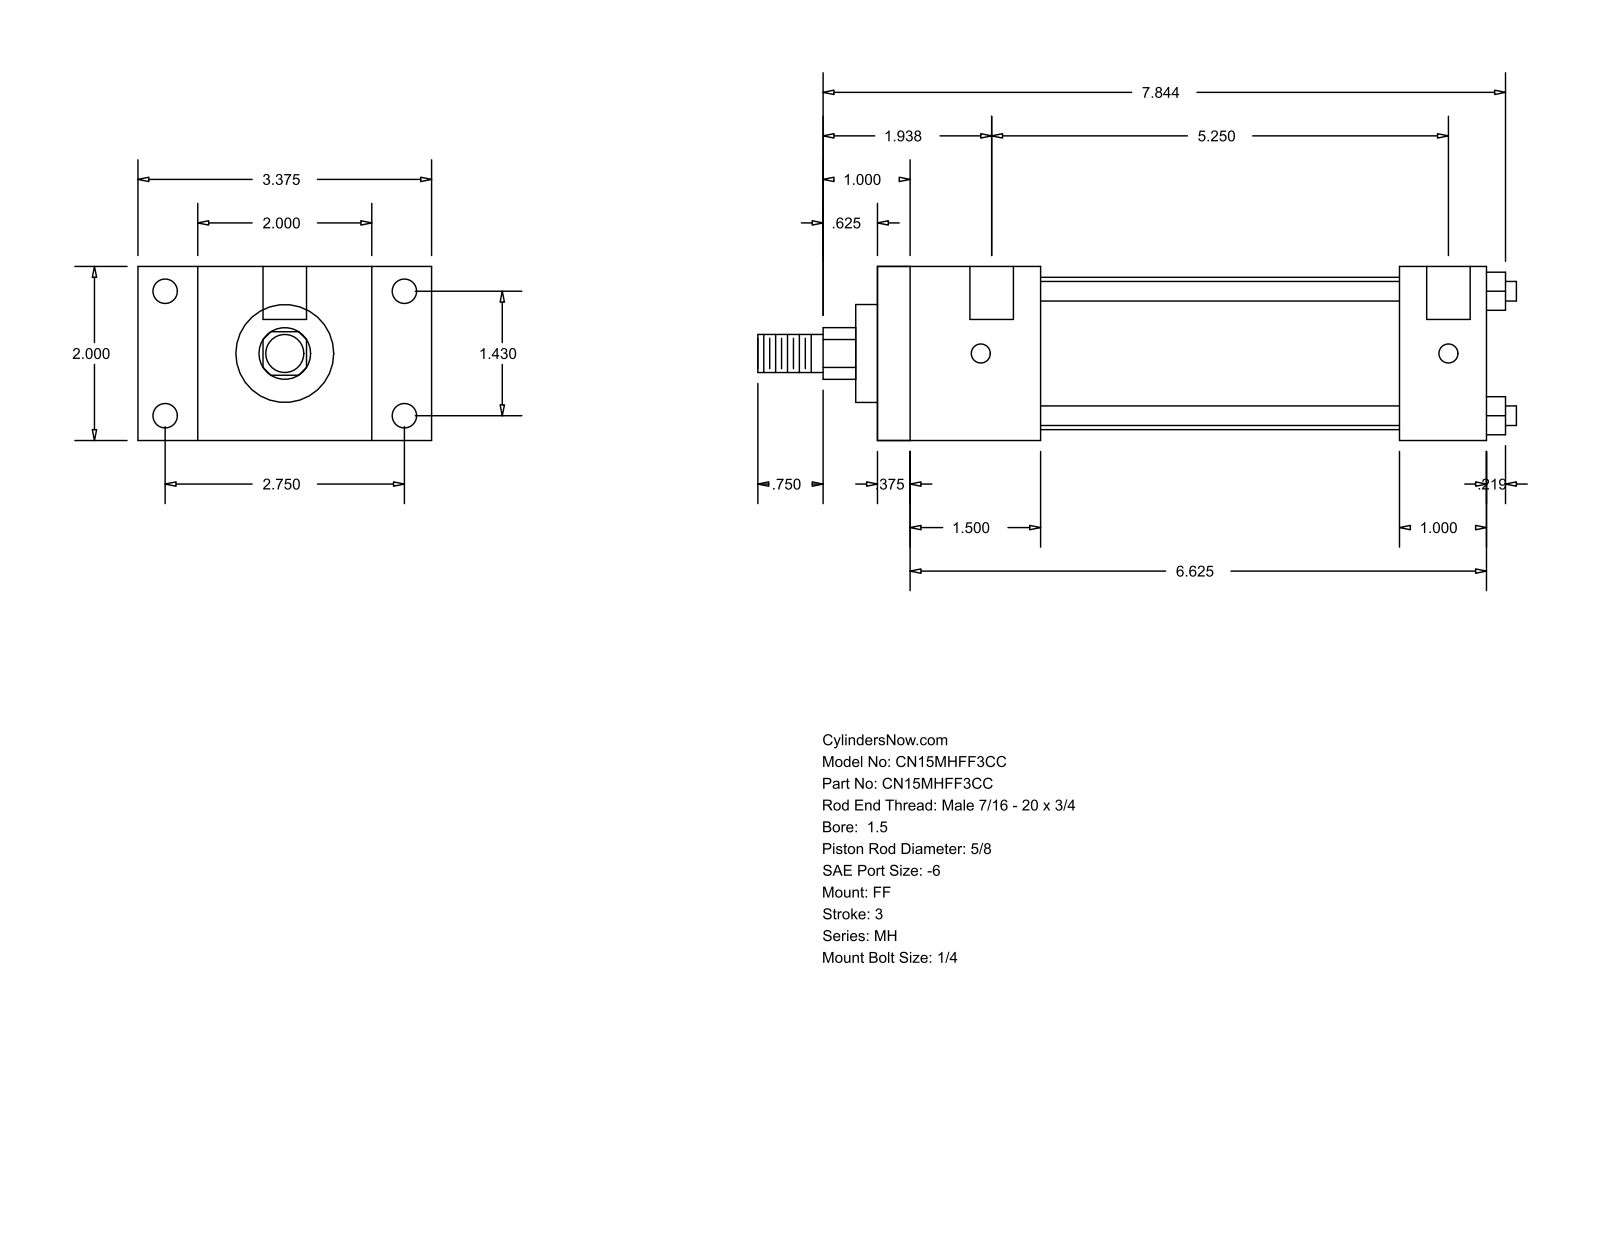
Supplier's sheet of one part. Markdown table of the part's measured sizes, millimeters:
| quantity | value |
| --- | --- |
| part name | MH_FF__0150_0.625 |
| STEP written by | GSSL Pune (CONFIG_CONTROL_DESIGN) |
| units | millimeters |
| bodies | 0 solids, 92 faces (64 planar, 28 cylindrical, 0 other) |
| overall size | 221.46 × 85.72 × 50.8 |
| round holes (diameter × count) | 5.56 × 4, 7.14 × 4, 12.7 × 2 |
| round bosses / shafts (diameter × count) | 5.71 × 4, 44.45 × 1, 28.57 × 1, 15.88 × 1, 11.11 × 1 |
| partial cylindrical surfaces (radius × count) | 7.54 × 1 |
| main face-to-face distances | 50.8, 177.8, 168.28, 9.52, 25.4, 17.46, 68.26, 47.62, 38.1, 130.18 |
| hole center spacings | 36.32, 69.84, 78.72, 136.52, 3.17, 133.35 |
